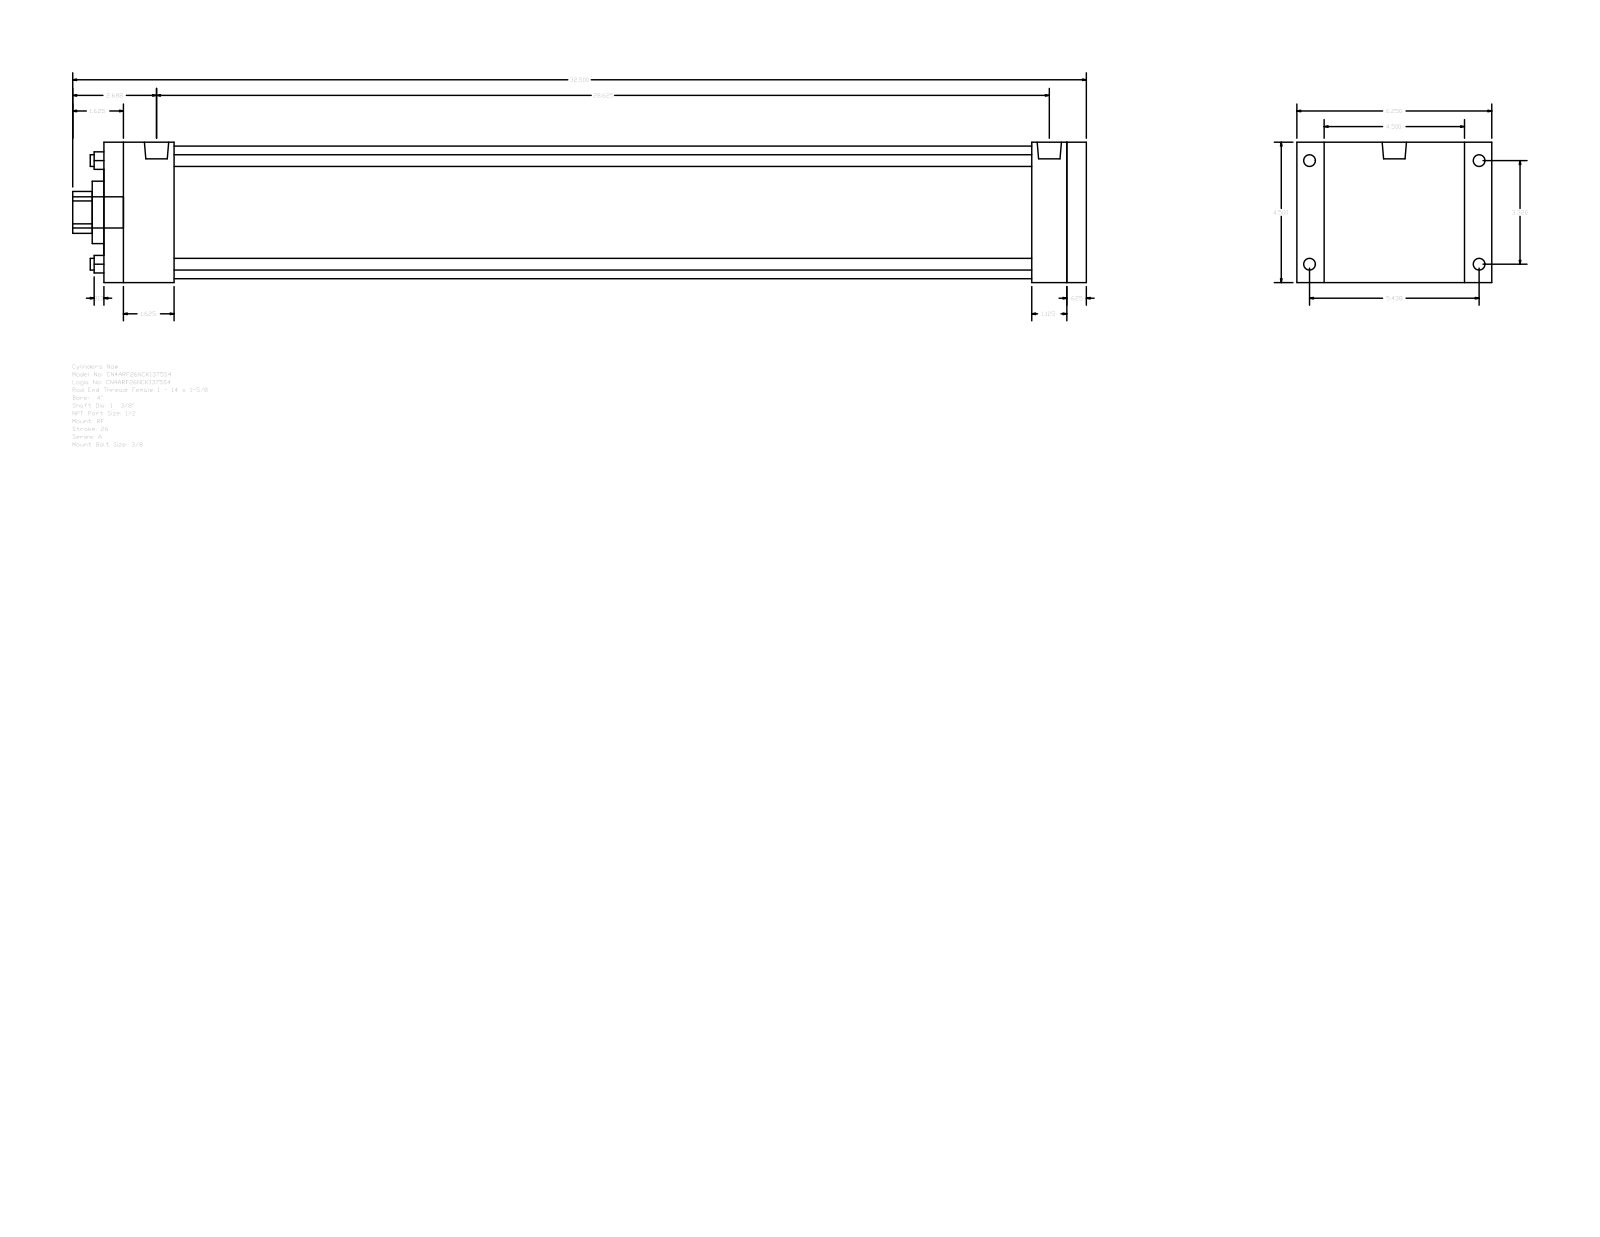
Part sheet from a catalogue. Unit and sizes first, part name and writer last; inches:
Units: inches
Overall size (bounding box): 32.5 × 6.25 × 4.5
Round holes (diameter × count): ⌀0.375 ×4, ⌀1.375 ×1, ⌀2 ×1, ⌀4.25 ×1
Round bosses / shafts (diameter × count): ⌀0.375 ×4, ⌀0.344 ×4, ⌀0.778 ×2, ⌀1 ×1
Partial cylindrical surfaces — rounded edges, fillets, slot ends (radius × count): R0.672 ×1
Main face-to-face distances: 4.5, 31.5, 0.625, 30.875, 1.125, 0.875, 5.375, 29.75, 1.75, 2.25
Hole centre spacings: 2.347, 3.32, 4.695
Bodies: 0 solids, 92 faces (64 planar, 28 cylindrical, 0 other)
Part name (STEP PRODUCT): A_RF__0400_1.375
STEP written by: GSSL Pune (CONFIG_CONTROL_DESIGN)
